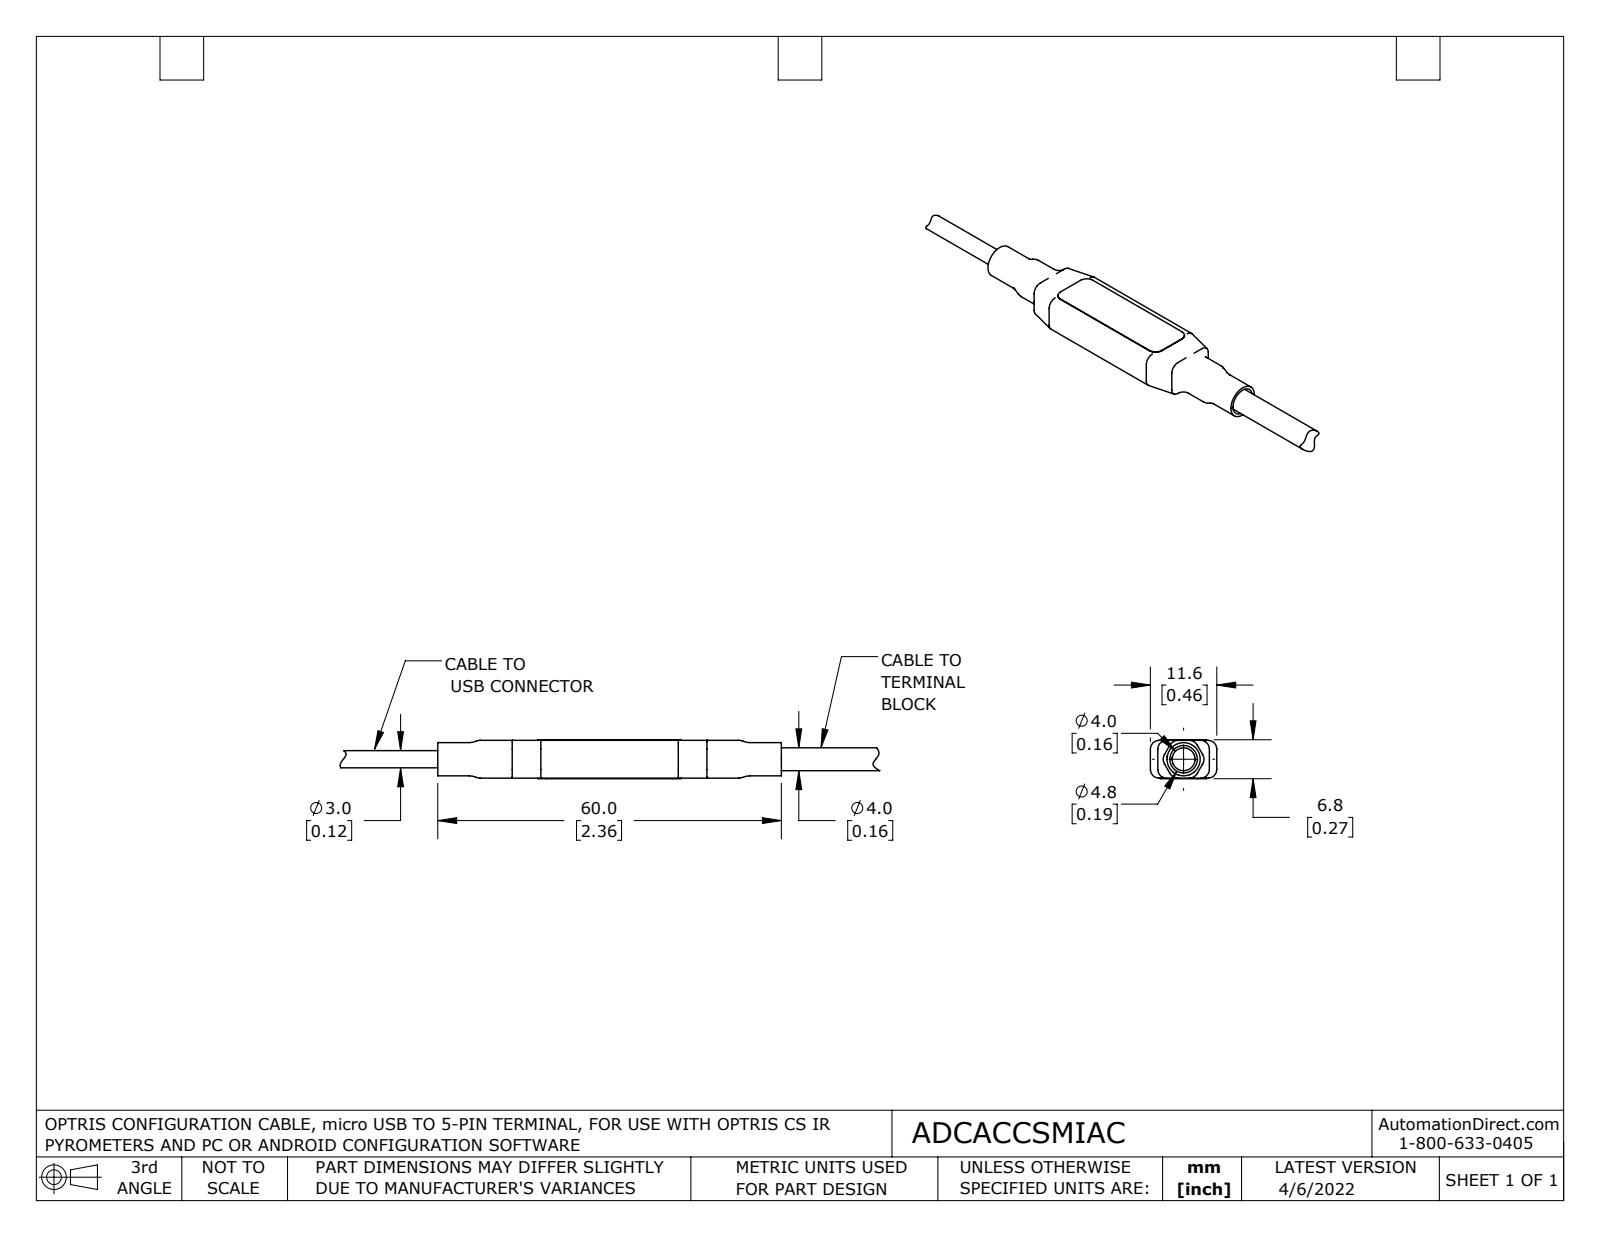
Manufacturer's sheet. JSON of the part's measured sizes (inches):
{"part_name": "ADCACCSMIAC fxt", "step_written_by": "SolidWorks 2021 (AUTOMOTIVE_DESIGN)", "units": "inches", "bodies": {"solids": 9, "faces": 825, "planar": 277, "cylindrical": 310, "other": 238}, "overall_size": [3.71, 0.457, 0.268], "volume_in3": 0.128, "surface_area_in2": 12.06, "round_holes": [[0.118, 2], [0.079, 1], [0.181, 1], [0.189, 1]], "round_bosses_or_shafts": [[0.031, 10], [0.035, 8], [0.02, 4], [0.228, 1], [0.205, 1], [0.197, 1], [0.157, 1]], "partial_cylinders_radius": [[0.02, 56], [0.012, 48], [0.008, 24], [0.039, 16], [0.059, 12], [0.043, 6], [0.063, 6], [0.031, 4]], "face_to_face_distances": [0.02, 0.024, 0.24, 0.22, 0.217, 0.197, 0.043, 0.26, 0.244, 0.264]}
